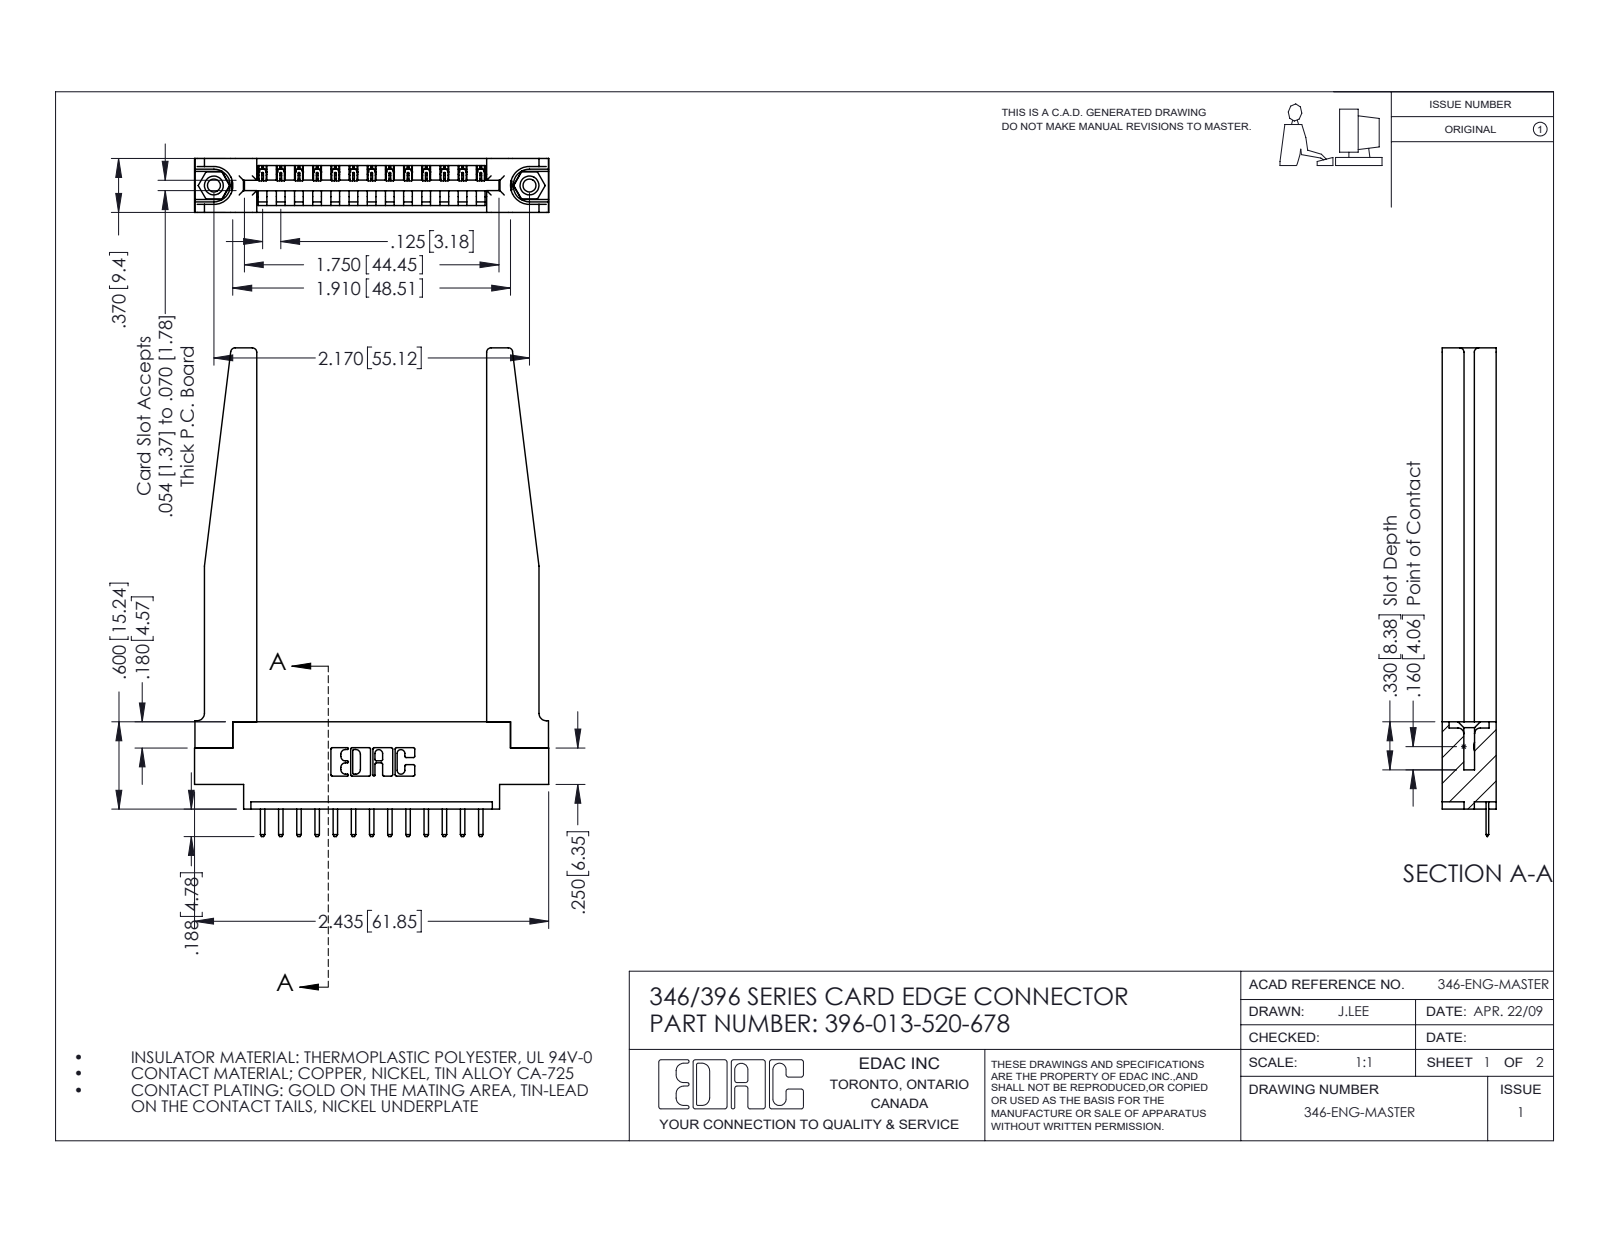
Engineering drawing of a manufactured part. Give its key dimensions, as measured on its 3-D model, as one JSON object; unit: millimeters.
{"part_name": "345-292-001_345-293-120; 346-220-078_345-220-078; 346 Part_0.170 Offset - 0.156 Dia-TH; 396-013-520-678 (+1 more)", "step_written_by": "SolidWorks 2016 (CONFIG_CONTROL_DESIGN)", "units": "millimeters", "bodies": {"solids": 18, "faces": 1166, "planar": 768, "cylindrical": 346, "other": 52}, "overall_size": [85.3, 61.8, 9.4], "volume_mm3": 12400, "surface_area_mm2": 13170, "round_holes": [[2.3, 2], [3.2, 2], [4, 2], [1.6, 1]], "round_bosses_or_shafts": [[3.9, 2]], "partial_cylinders_radius": [[0.3, 28], [0.2, 26], [0.3, 22], [0.8, 8], [0.2, 6], [0.8, 6], [0.7, 3], [0.8, 2]], "face_to_face_distances": [9.4, 3.8, 1.8, 3.8, 1.2, 8.2, 2.6, 5.6, 4.4, 6.4], "hole_center_spacings": [6.2, 49.9, 55.1]}
